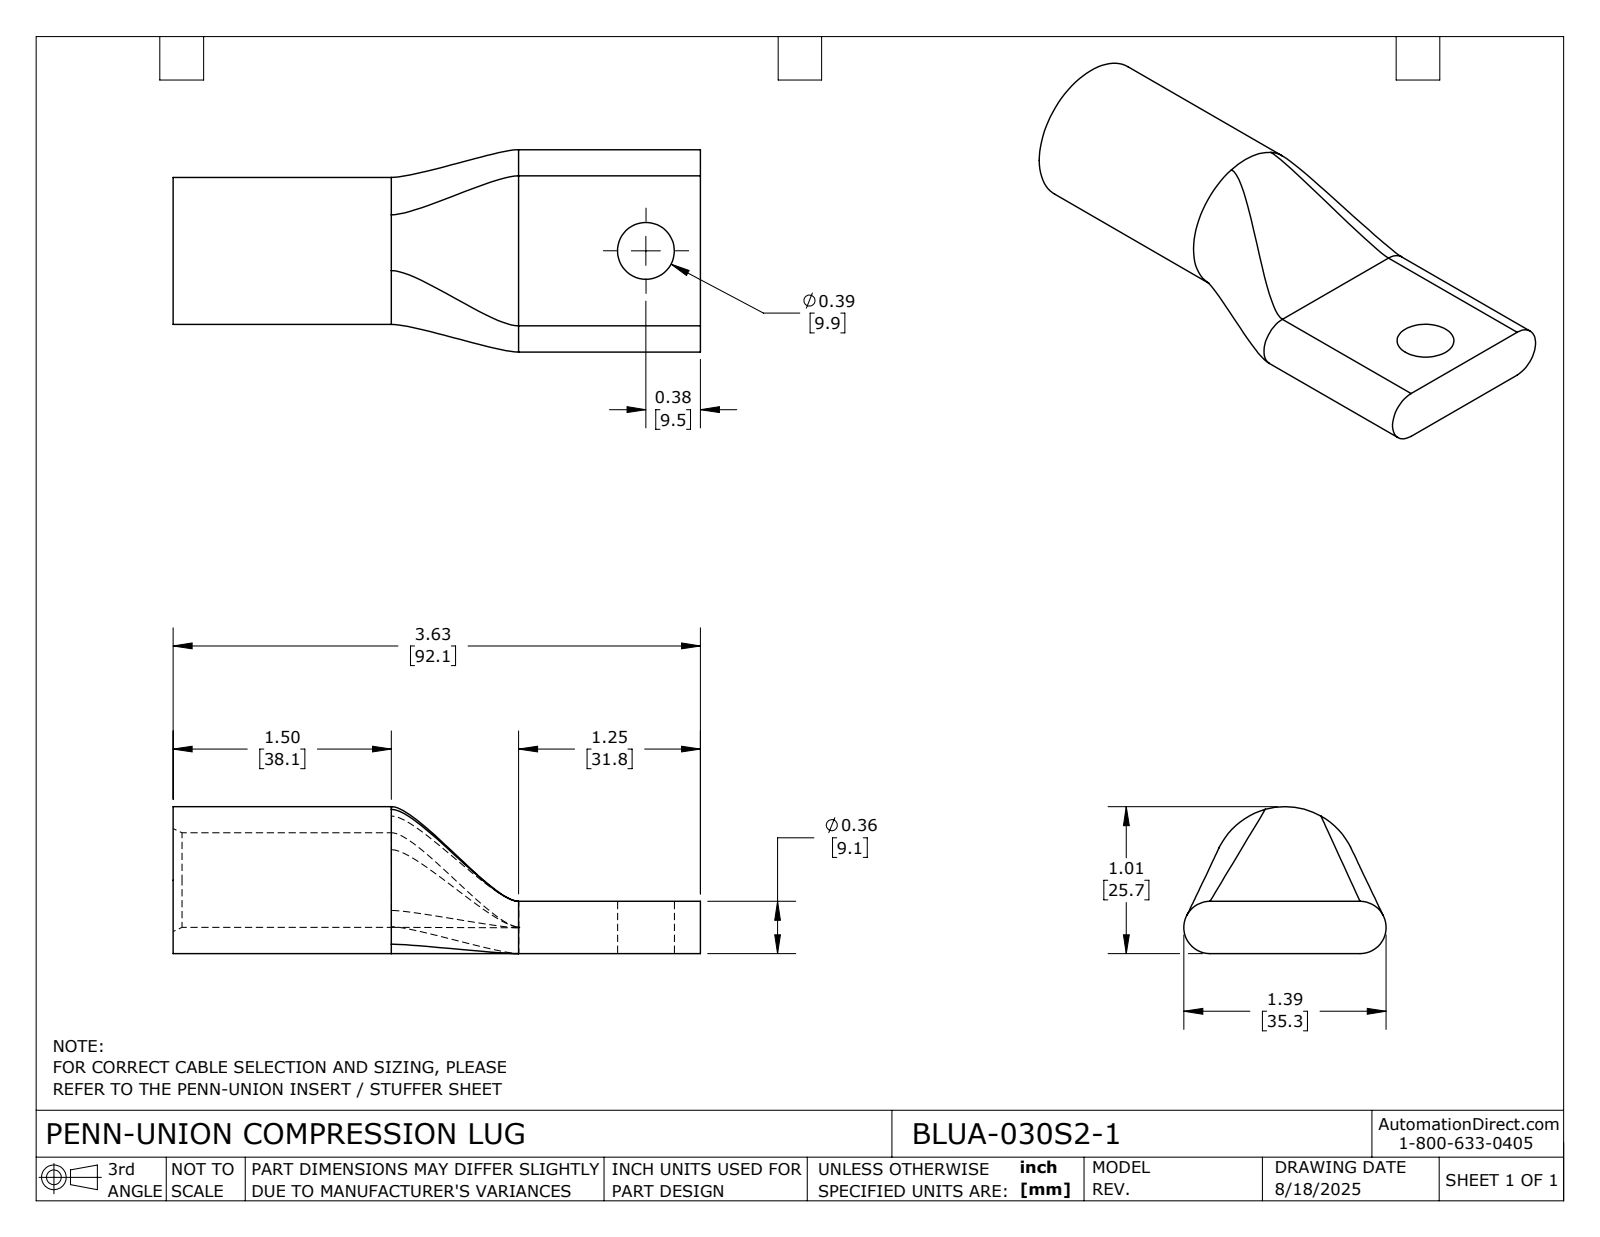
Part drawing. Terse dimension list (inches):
name: BLUA-030S2-1
written by: SolidWorks 2024 (CONFIG_CONTROL_DESIGN)
unit: in
bodies: 1 solid, 24 faces (5 planar, 9 cylindrical, 10 other)
size: 3.625 × 1.391 × 1.01
volume: 1.658 in³; area: 17.83 in²
holes: 1× ⌀0.391, 1× ⌀0.65
bosses: 1× ⌀1.01
rounds: 2× R0.18
face distances: 0.359, 3.625, 2.375, 1.25
